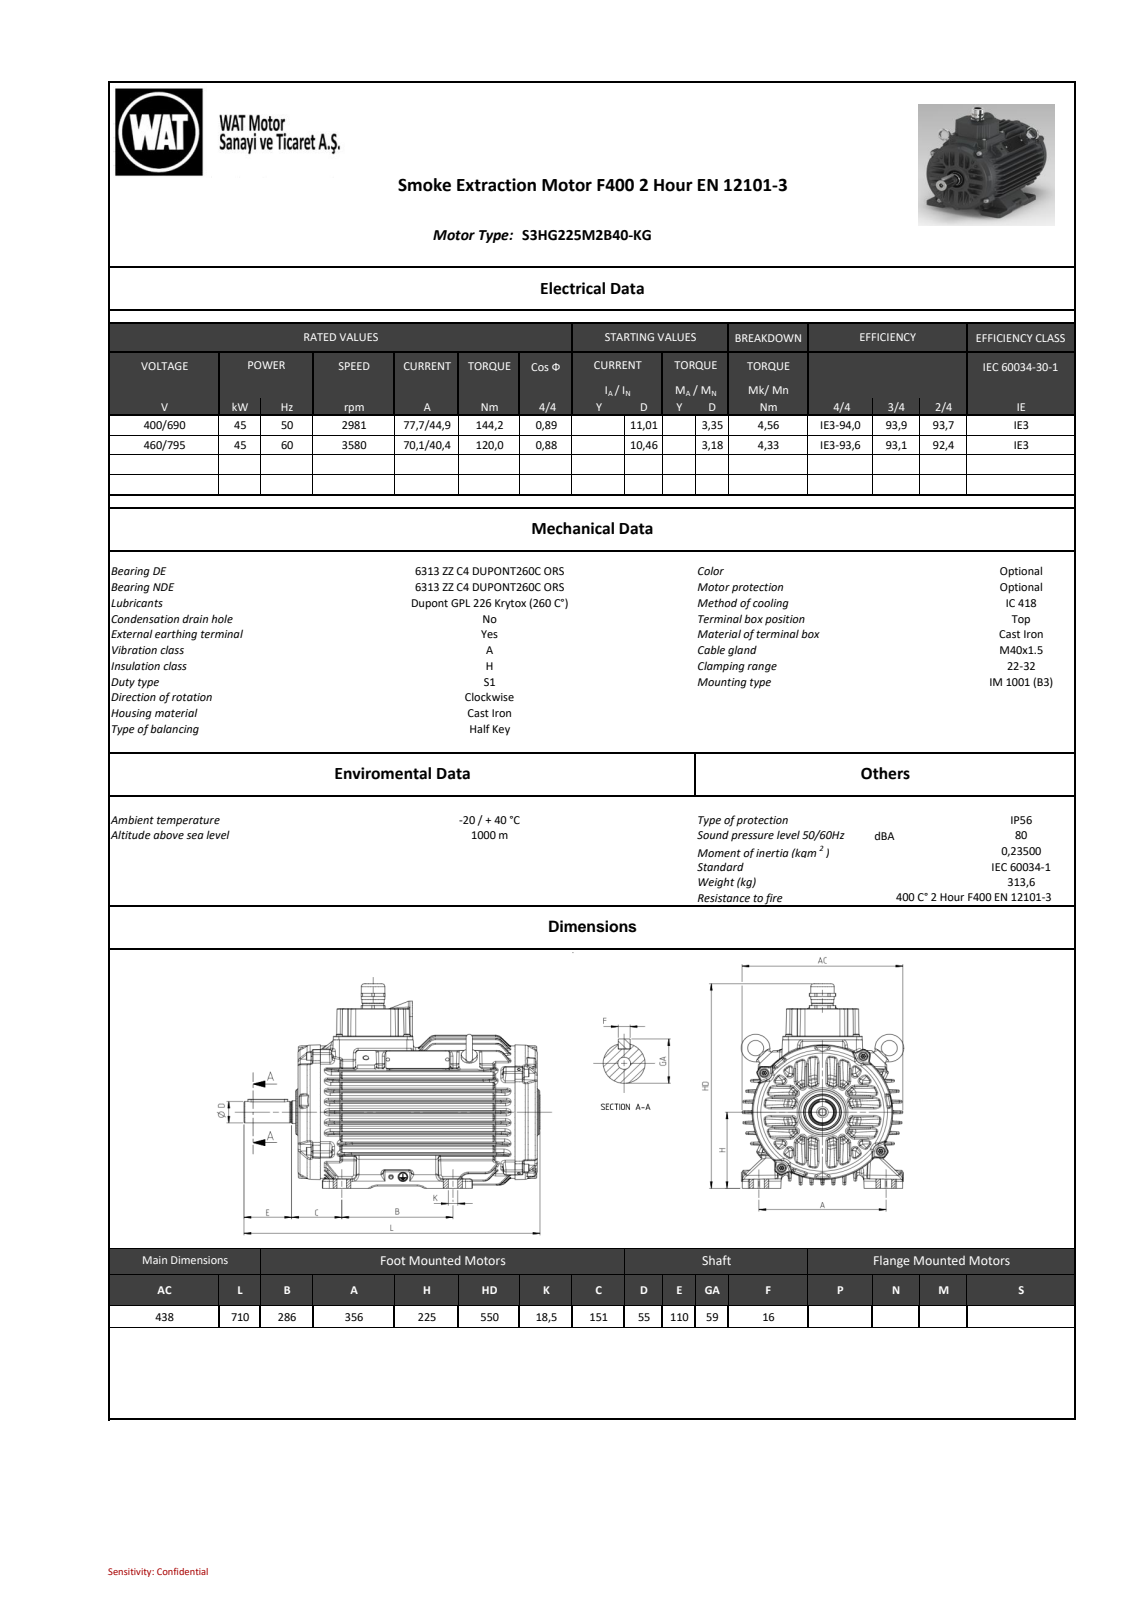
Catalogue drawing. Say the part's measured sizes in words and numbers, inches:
The part is named "260381480CFDz4ae". Its 3-D file was written by "SIEMENS PLM Software NX 11.0 (AUTOMOTIVE_DESIGN)". It is 0 solids with 7186 faces: 932 planar, 1618 cylindrical and 4636 other. Overall it measures 27.953 by 21.654 by 17.441 inches. Round holes: 10 of diameter 0.551, 5 of diameter 0.268, 1 of diameter 0.827, 1 of diameter 1.26, 1 of diameter 3.228, 1 of diameter 3.478, 1 of diameter 3.937. Round bosses or shafts: 8 of diameter 1.181, 4 of diameter 0.945, 4 of diameter 0.932, 4 of diameter 0.472, 2 of diameter 1.378, 1 of diameter 14.646, 1 of diameter 3.019, 1 of diameter 2.559. Partial cylindrical surfaces (rounded edges, fillets, slot ends): 332 of radius 0.157, 233 of radius 0.079, 146 of radius 0.197, 137 of radius 0.118, 82 of radius 0.236, 44 of radius 0.024, 19 of radius 0.394, 12 of radius 0.02. The main face-to-face distances are 0.685, 6.287, 0.682, 7.654, 1.374, 5.599, 0.688, 3.479, 2.065, 1.379. The hole center spacings are 7.795, 11.024, 2.707, 8.943, 12.771, 15.354, 15.591.
